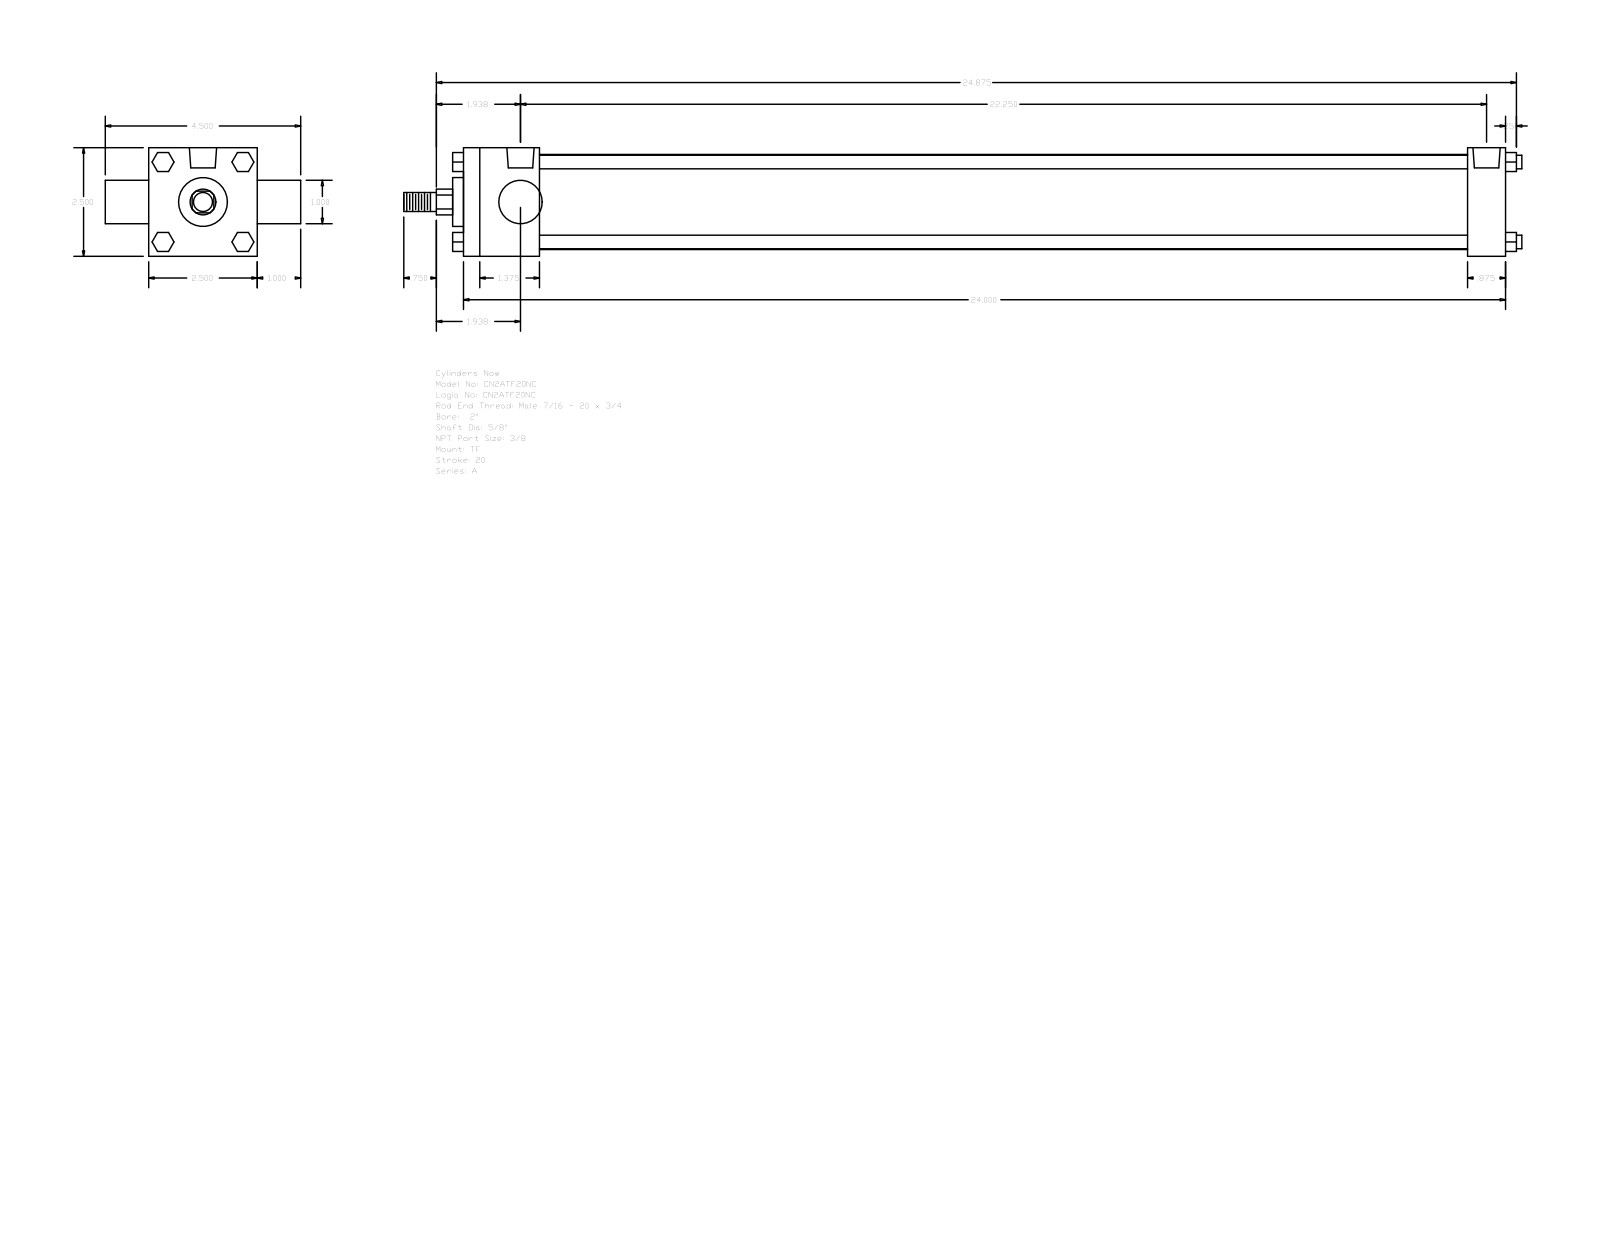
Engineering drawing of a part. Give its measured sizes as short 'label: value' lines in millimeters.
name: A_TF__0200_0.625
written by: GSSL Pune (CONFIG_CONTROL_DESIGN)
unit: mm
bodies: 0 solids, 120 faces (92 planar, 28 cylindrical, 0 other)
size: 654.05 × 114.3 × 63.5
holes: 3× ⌀5.56, 2× ⌀15.93
bosses: 4× ⌀7.94, 1× ⌀55.63, 1× ⌀28.57, 1× ⌀25.4, 1× ⌀15.88, 1× ⌀11.11
rounds: 1× R7.54
face distances: 63.5, 609.6, 44.45, 587.37, 542.92, 565.15, 22.23, 25.4, 88.9, 6.35
hole spacings: 3.97, 3.98, 557.2, 561.17, 561.18, 565.15
